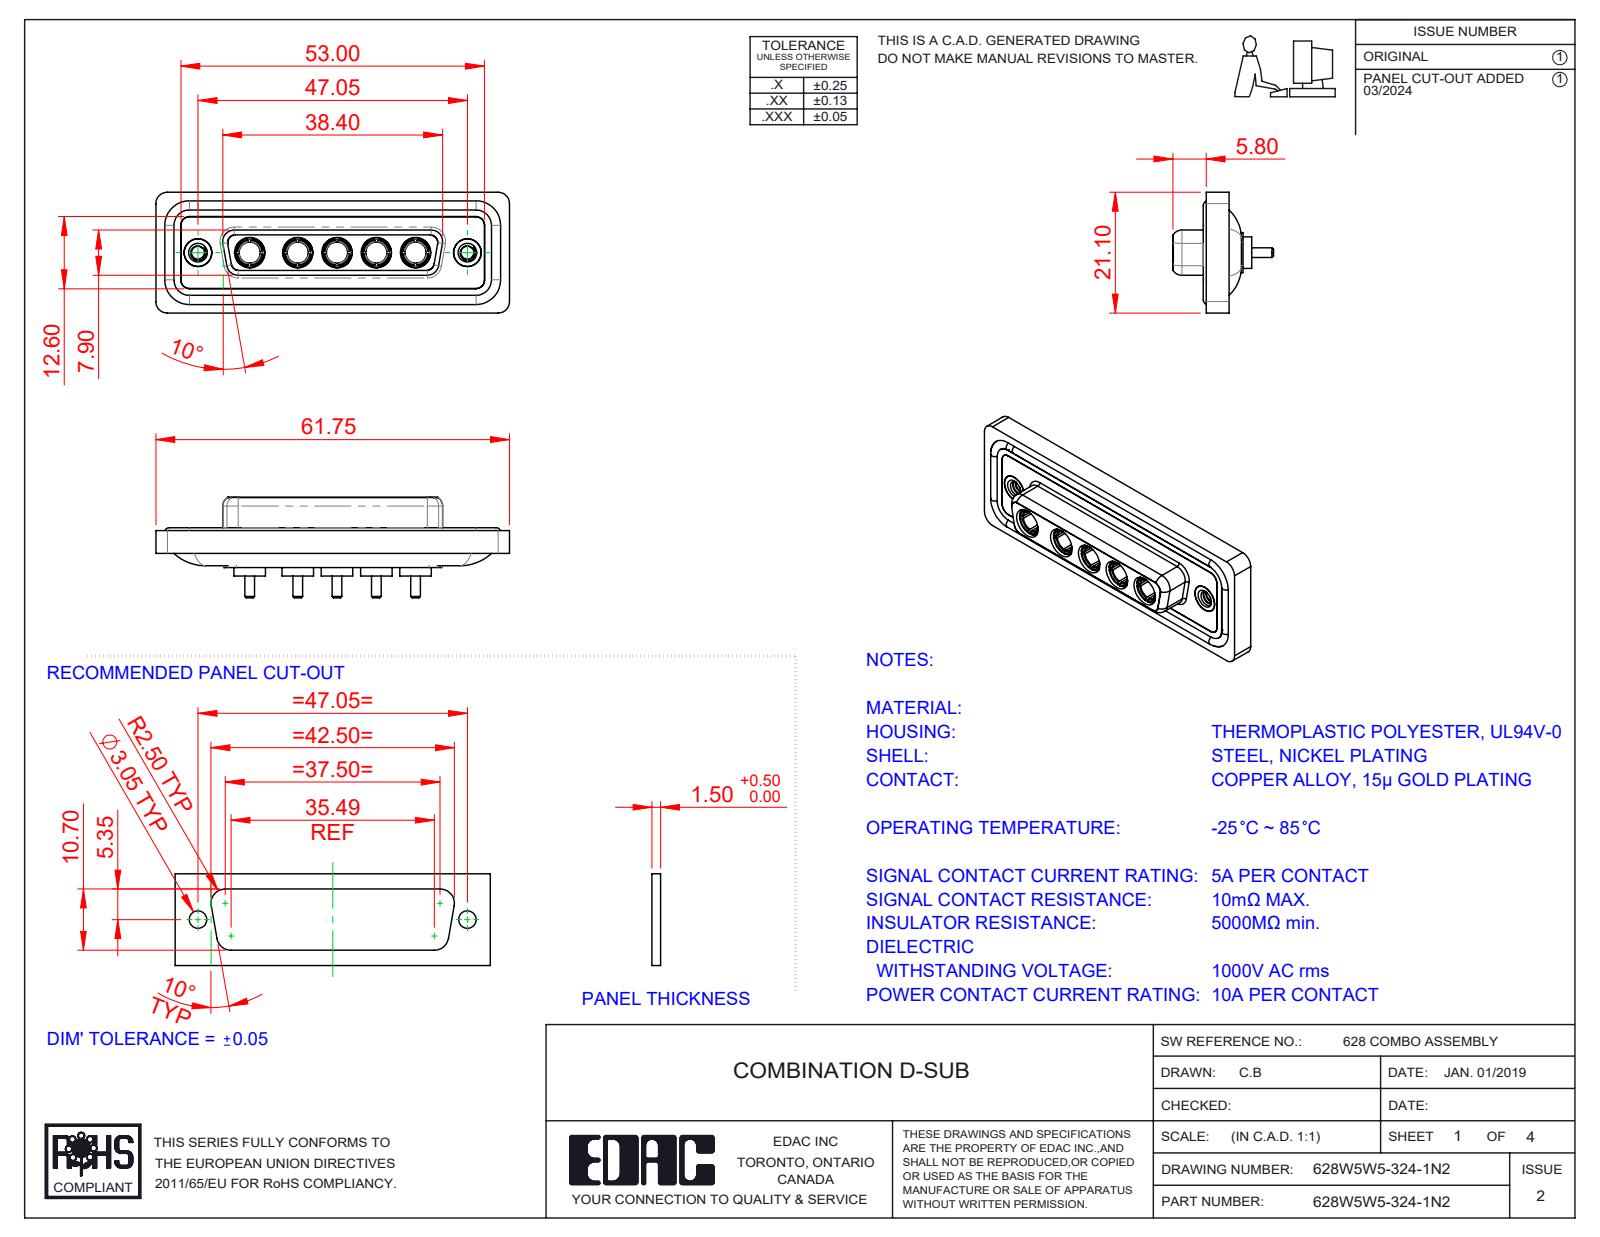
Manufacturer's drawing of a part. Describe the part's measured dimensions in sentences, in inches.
The part is named "628Combo Shell Front_25 Contacts; 628Combo Housing_5W5; 628Combo Shell Rear_25 Contacts; 628Combo Threaded Rivet_2 (+3 more)". Its 3-D file was written by "SolidWorks 2023 (CONFIG_CONTROL_DESIGN)". It is 17 solids with 756 faces: 250 planar, 303 cylindrical and 203 other. Overall it measures 2.431 by 0.831 by 0.691 inches. Its volume is 0.494 cubic inches and its surface area 20.7 square inches. Round holes: 7 of diameter 0.191, 5 of diameter 0.146, 5 of diameter 0.209, 2 of diameter 0.089, 2 of diameter 0.157, 2 of diameter 0.159, 2 of diameter 0.197. Round bosses or shafts: 5 of diameter 0.217, 5 of diameter 0.205, 5 of diameter 0.195, 5 of diameter 0.187, 5 of diameter 0.148, 5 of diameter 0.067, 4 of diameter 0.063, 2 of diameter 0.195. Partial cylindrical surfaces (rounded edges, fillets, slot ends): 22 of radius 0.059, 18 of radius 0.079, 8 of radius 0.053, 8 of radius 0.063, 5 of radius 0.083, 4 of radius 0.01, 4 of radius 0.02, 4 of radius 0.024. The main face-to-face distances are 0.016, 0.071, 0.293, 0.222, 0.02, 0.278, 0.26, 0.063, 0.043, 0.059. The hole center spacings are 0.27, 0.356, 0.54, 1.496, 0.33, 0.6, 0.626, 0.686.
